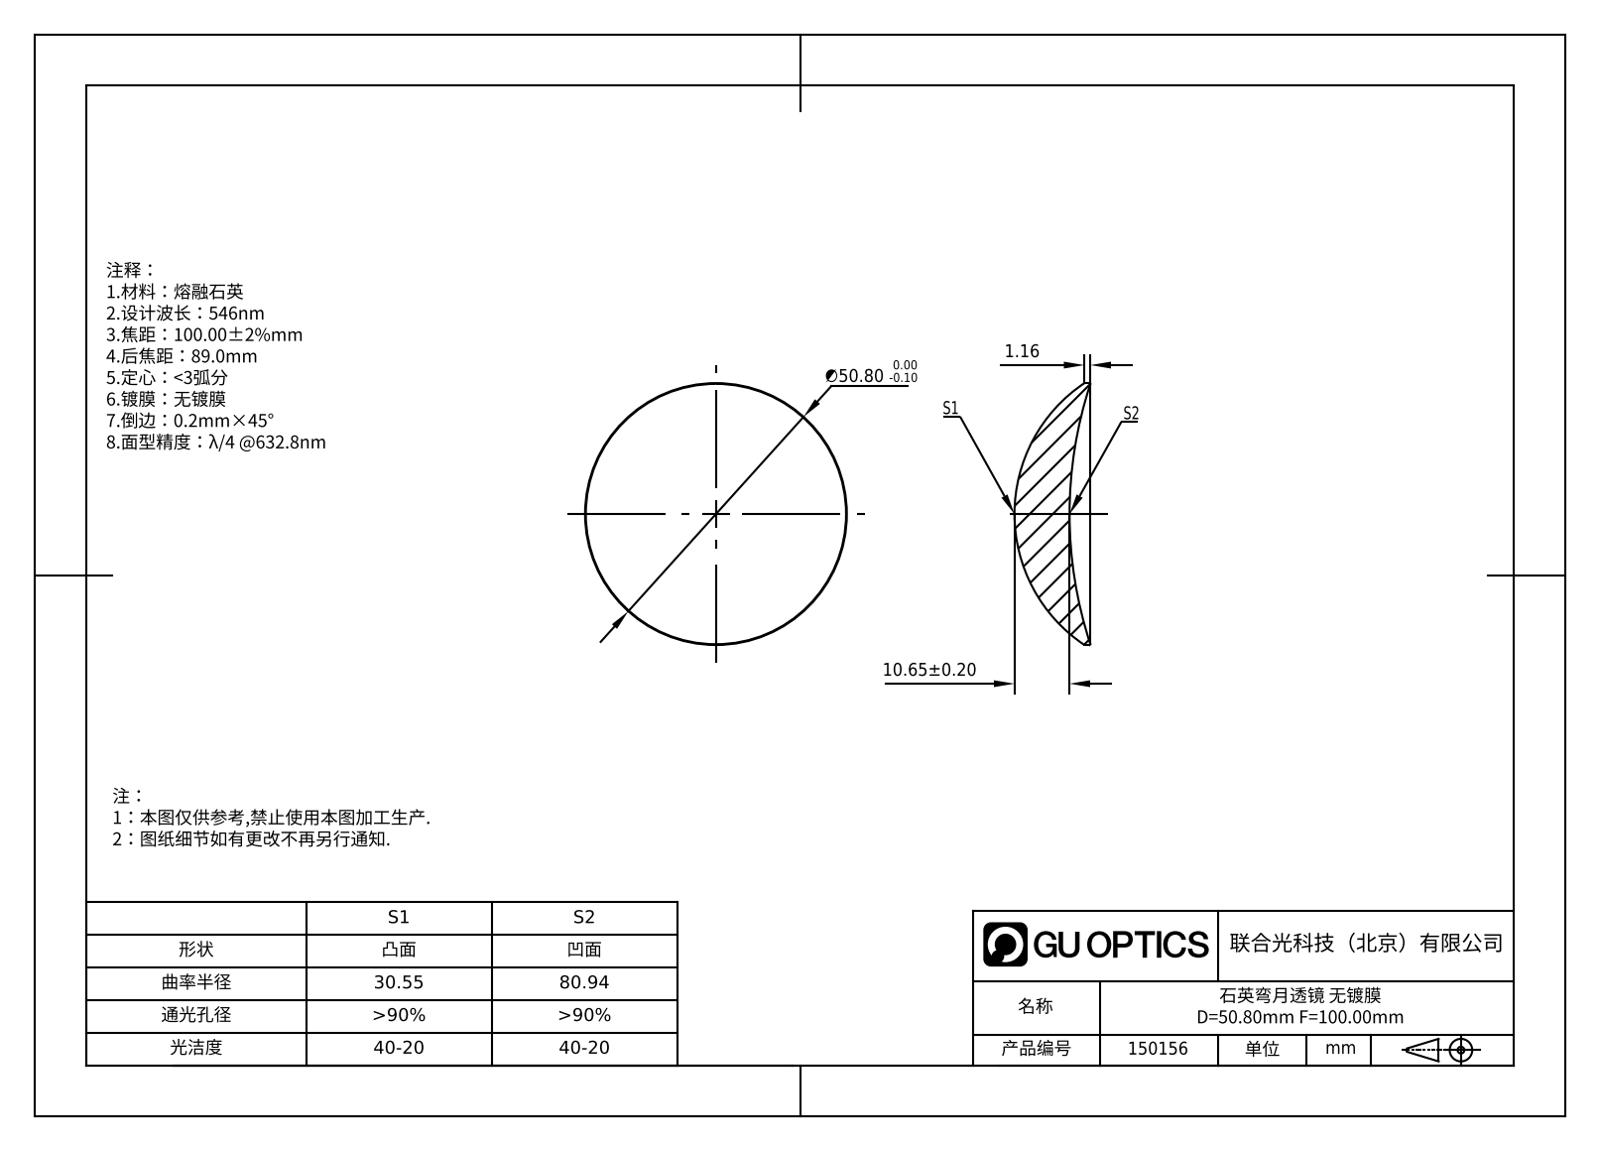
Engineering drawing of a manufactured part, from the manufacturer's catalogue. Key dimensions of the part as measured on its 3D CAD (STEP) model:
Part name (STEP PRODUCT): GLM2-050B-100
STEP written by: SolidWorks 2022 (AUTOMOTIVE_DESIGN)
Units: millimetres
Bodies: 1 solid, 8 faces (0 planar, 2 cylindrical, 6 other)
Overall size (bounding box): 50.8 × 50.8 × 14.73
Volume: 13 318 mm³ · Surface area: 4 853 mm²
Round bosses / shafts (diameter × count): ⌀50.8 ×1
